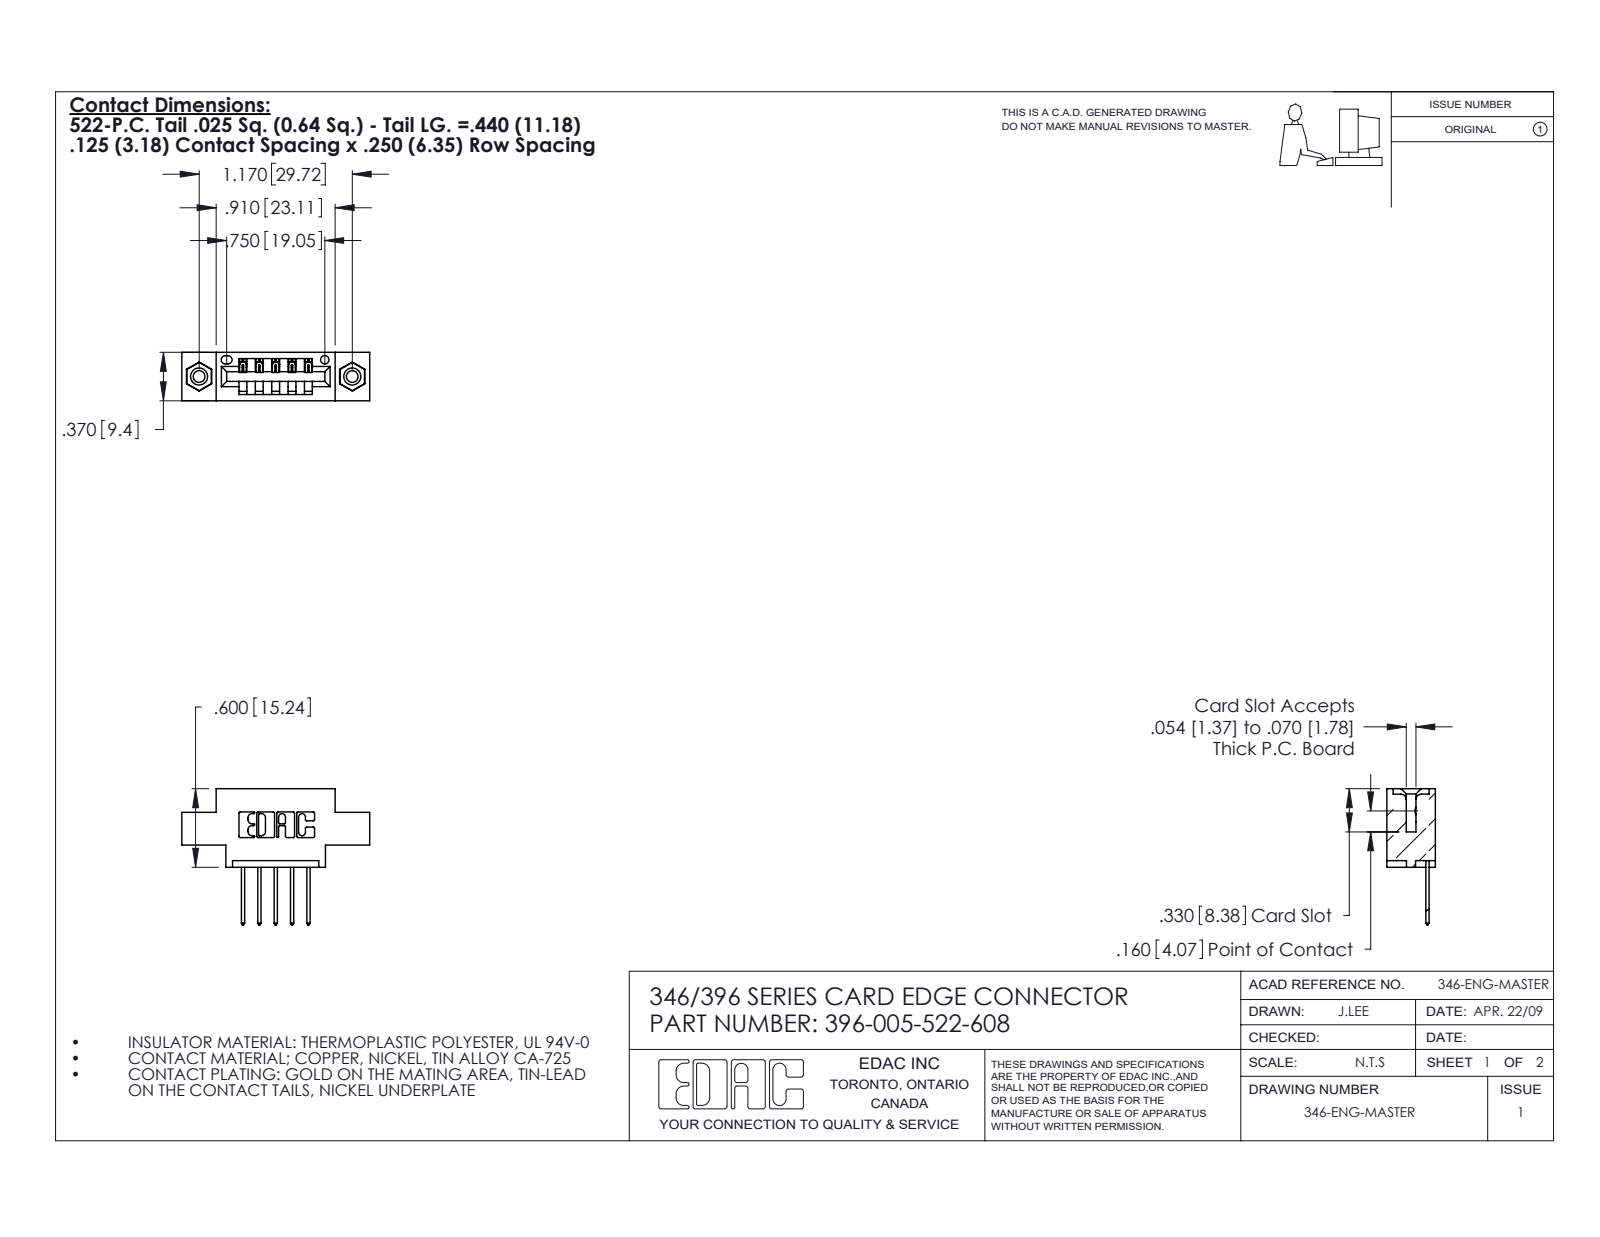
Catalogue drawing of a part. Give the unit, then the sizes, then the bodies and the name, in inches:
Units: inches
Overall size (bounding box): 1.435 × 1.04 × 0.37
Round holes (diameter × count): ⌀0.089 ×2, ⌀0.125 ×2, ⌀0.156 ×2, ⌀0.064 ×1
Round bosses / shafts (diameter × count): ⌀0.155 ×2
Partial cylindrical surfaces — rounded edges, fillets, slot ends (radius × count): R0.01 ×22, R0.006 ×10, R0.01 ×10, R0.007 ×6, R0.031 ×6, R0.026 ×3, R0.031 ×2, R0.04 ×2
Main face-to-face distances: 0.25, 0.37, 0.048, 0.322, 0.222, 0.148, 0.1, 0.174, 0.55, 0.072
Hole centre spacings: 0.246, 0.969, 1.17
Volume: 0.188 in³ · Surface area: 5.646 in²
Bodies: 8 solids, 476 faces (312 planar, 148 cylindrical, 16 other)
Part name (STEP PRODUCT): 345-292-001_345-293-122; 345-250-001_345-250-003-102; 346 Part_0.170 Offset - 0.156 Dia-TI; 396-005-522-608
STEP written by: SolidWorks 2020 (CONFIG_CONTROL_DESIGN)
